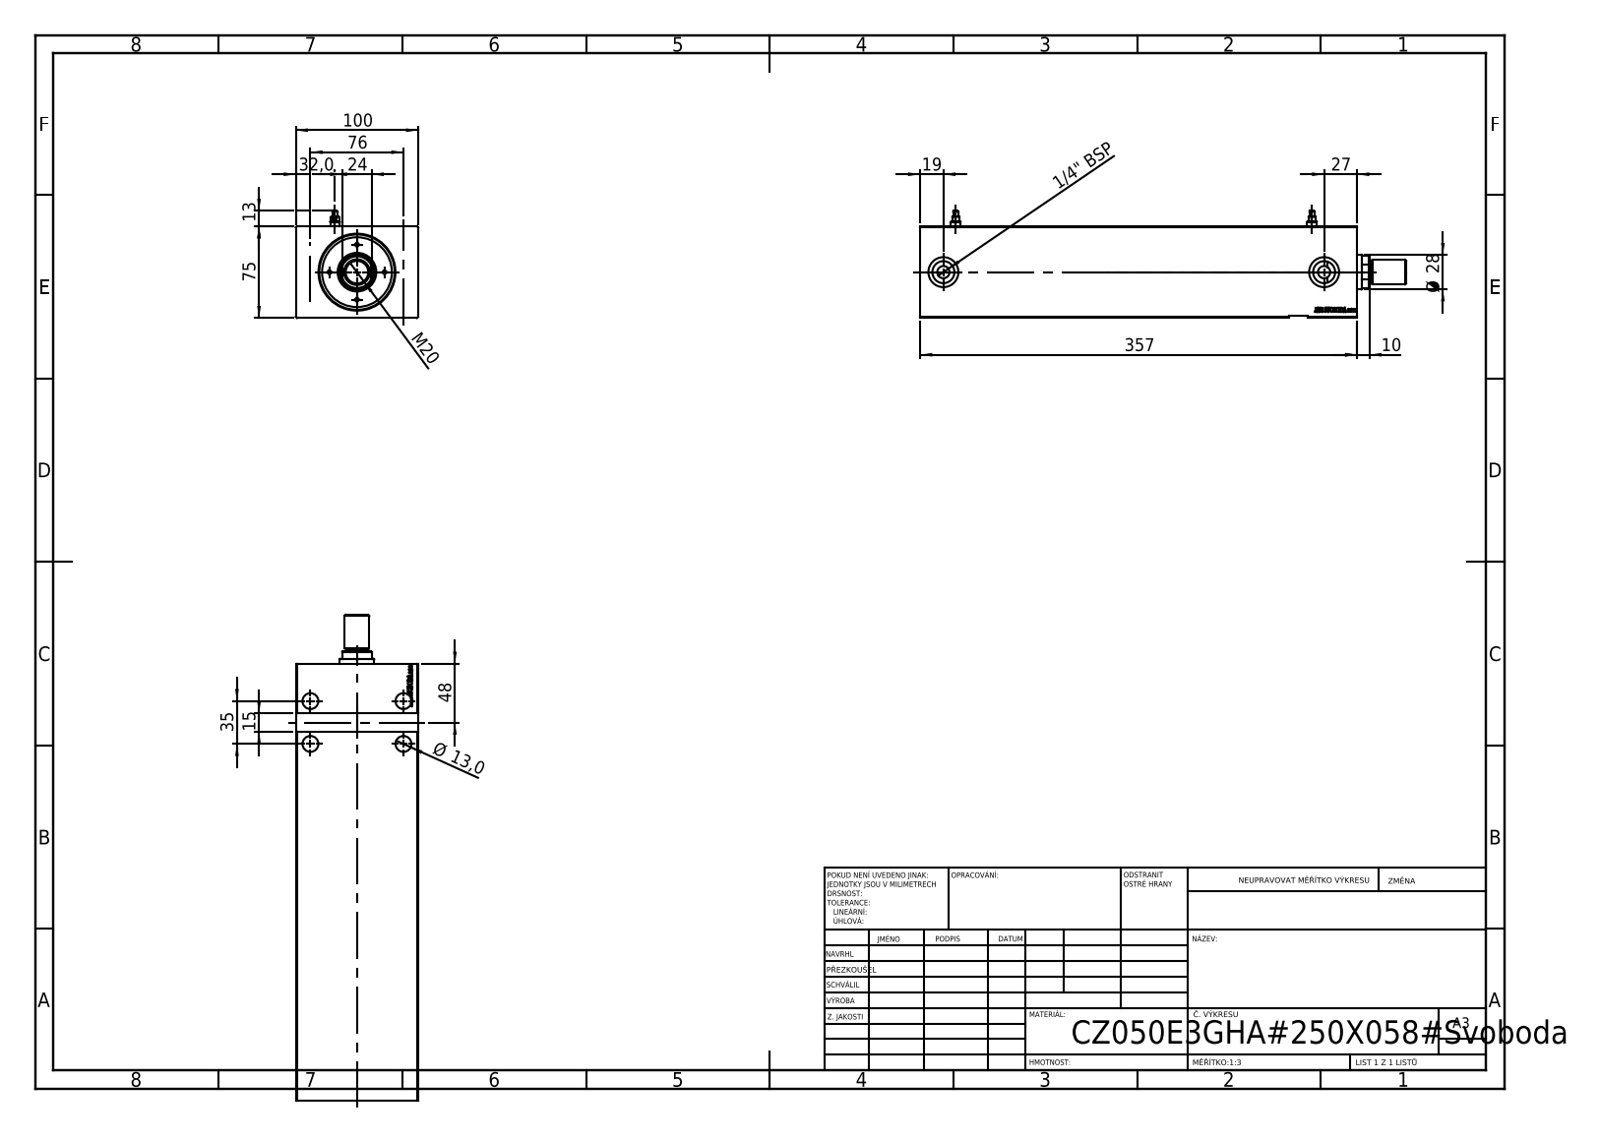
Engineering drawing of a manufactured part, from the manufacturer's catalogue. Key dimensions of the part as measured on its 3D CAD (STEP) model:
STEP written by: SolidWorks 2019 (CONFIG_CONTROL_DESIGN)
Units: millimetres
Bodies: 1 solid, 776 faces (375 planar, 31 cylindrical, 370 other)
Overall size (bounding box): 357 × 100 × 75
Volume: 1 951 000 mm³ · Surface area: 205 640 mm²
Round holes (diameter × count): ⌀13 ×4, ⌀8 ×2, ⌀10 ×2, ⌀18 ×2, ⌀24.5 ×2, ⌀36 ×1, ⌀50 ×1, ⌀61.5 ×1
Main face-to-face distances: 75, 100, 357, 339.2, 17.8, 2, 73, 356.8, 17.6, 10
Hole centre spacings: 35, 76, 83.67, 21.03, 34.82, 56.38, 62.84, 263.26
